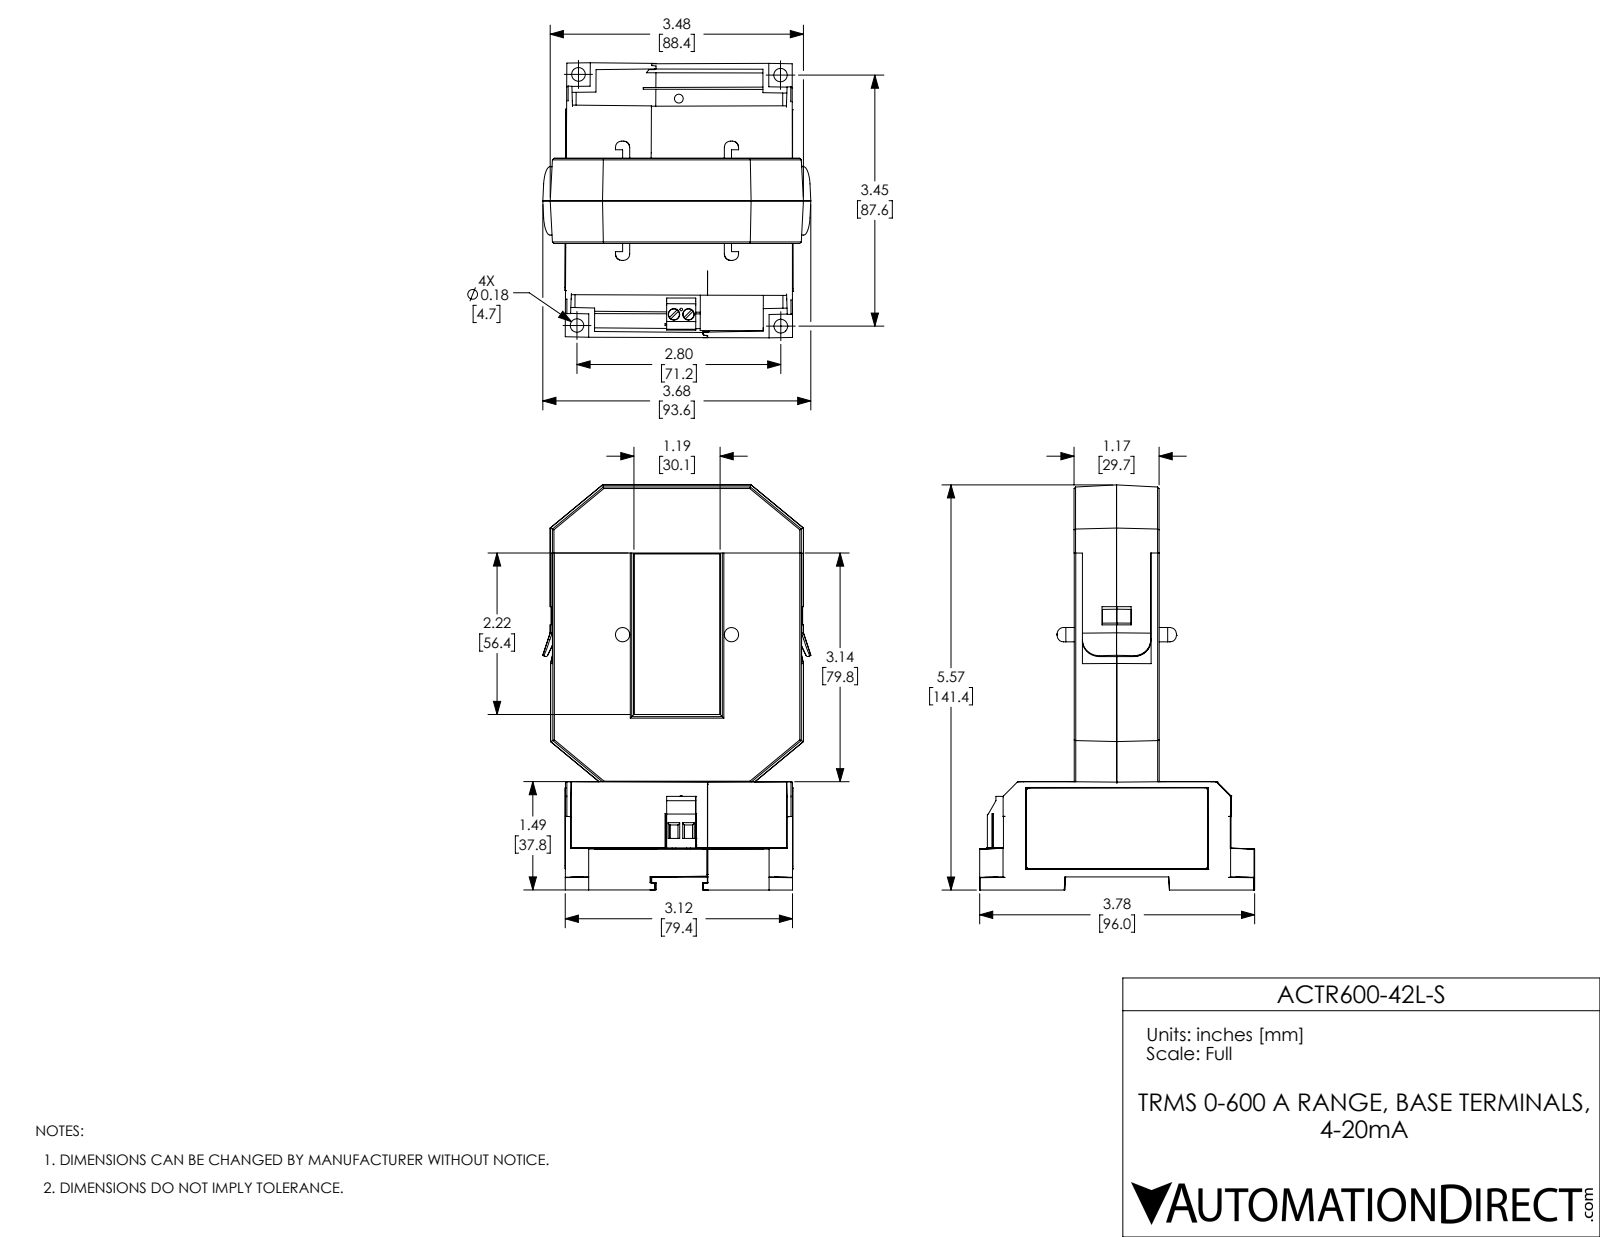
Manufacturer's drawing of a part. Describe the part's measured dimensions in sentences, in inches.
The part is named "ACTR600-42L-S". Its 3-D file was written by "SolidWorks 2017 (AUTOMOTIVE_DESIGN)". It is 15 solids with 1439 faces: 1182 planar, 144 cylindrical and 113 other. Overall it measures 5.569 by 3.781 by 3.684 inches. Its volume is 7.995 cubic inches and its surface area 222.6 square inches. Round holes: 2 of diameter 0.157, 2 of diameter 0.256. Round bosses or shafts: 2 of diameter 0.197, 2 of diameter 0.15, 2 of diameter 0.051, 1 of diameter 0.018. Partial cylindrical surfaces (rounded edges, fillets, slot ends): 30 of radius 0.02, 12 of radius 0.039, 10 of radius 0.006, 8 of radius 0.05, 6 of radius 0.025, 4 of radius 0.008, 4 of radius 0.01, 4 of radius 0.02. The main face-to-face distances are 0.071, 1.097, 1.168, 1.026, 0.081, 0.585, 0.075, 0.08, 2.328, 1.095. The hole center spacings are 0.2, 0.42, 1.563, 1.57, 1.581, 1.604.
